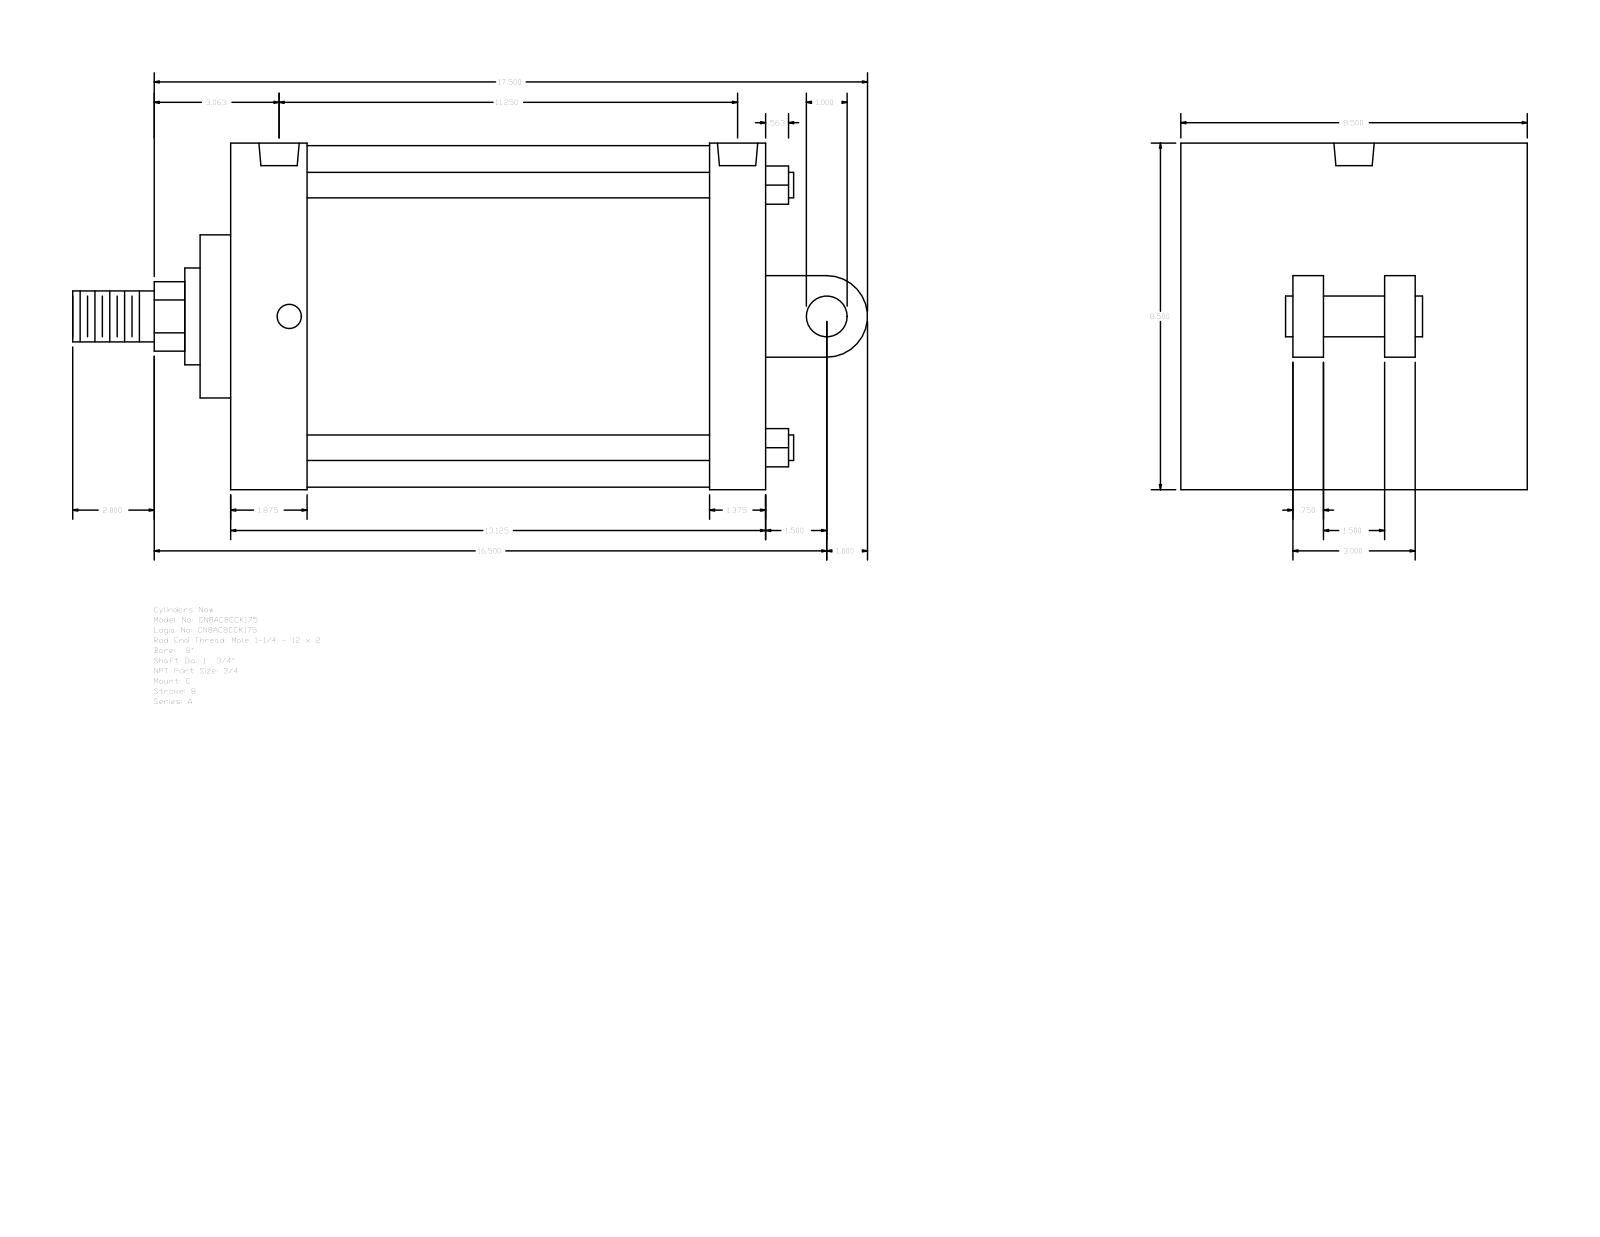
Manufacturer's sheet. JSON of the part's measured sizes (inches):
{"part_name": "A_C__0800_1.75", "step_written_by": "GSSL Pune (CONFIG_CONTROL_DESIGN)", "units": "inches", "bodies": {"solids": 0, "faces": 104, "planar": 75, "cylindrical": 29, "other": 0}, "overall_size": [19.5, 8.5, 8.5], "round_holes": [[0.594, 4], [0.989, 2]], "round_bosses_or_shafts": [[0.625, 4], [8.375, 1], [2.375, 1], [1.75, 1], [1.25, 1], [1, 1]], "partial_cylinders_radius": [[0.852, 1], [1, 1]], "face_to_face_distances": [13.125, 8.5, 0.75, 2.25, 1.875, 11.25, 11.75, 9.875, 1.375, 2.75], "hole_center_spacings": [0.25, 10.75, 11, 11.25]}
